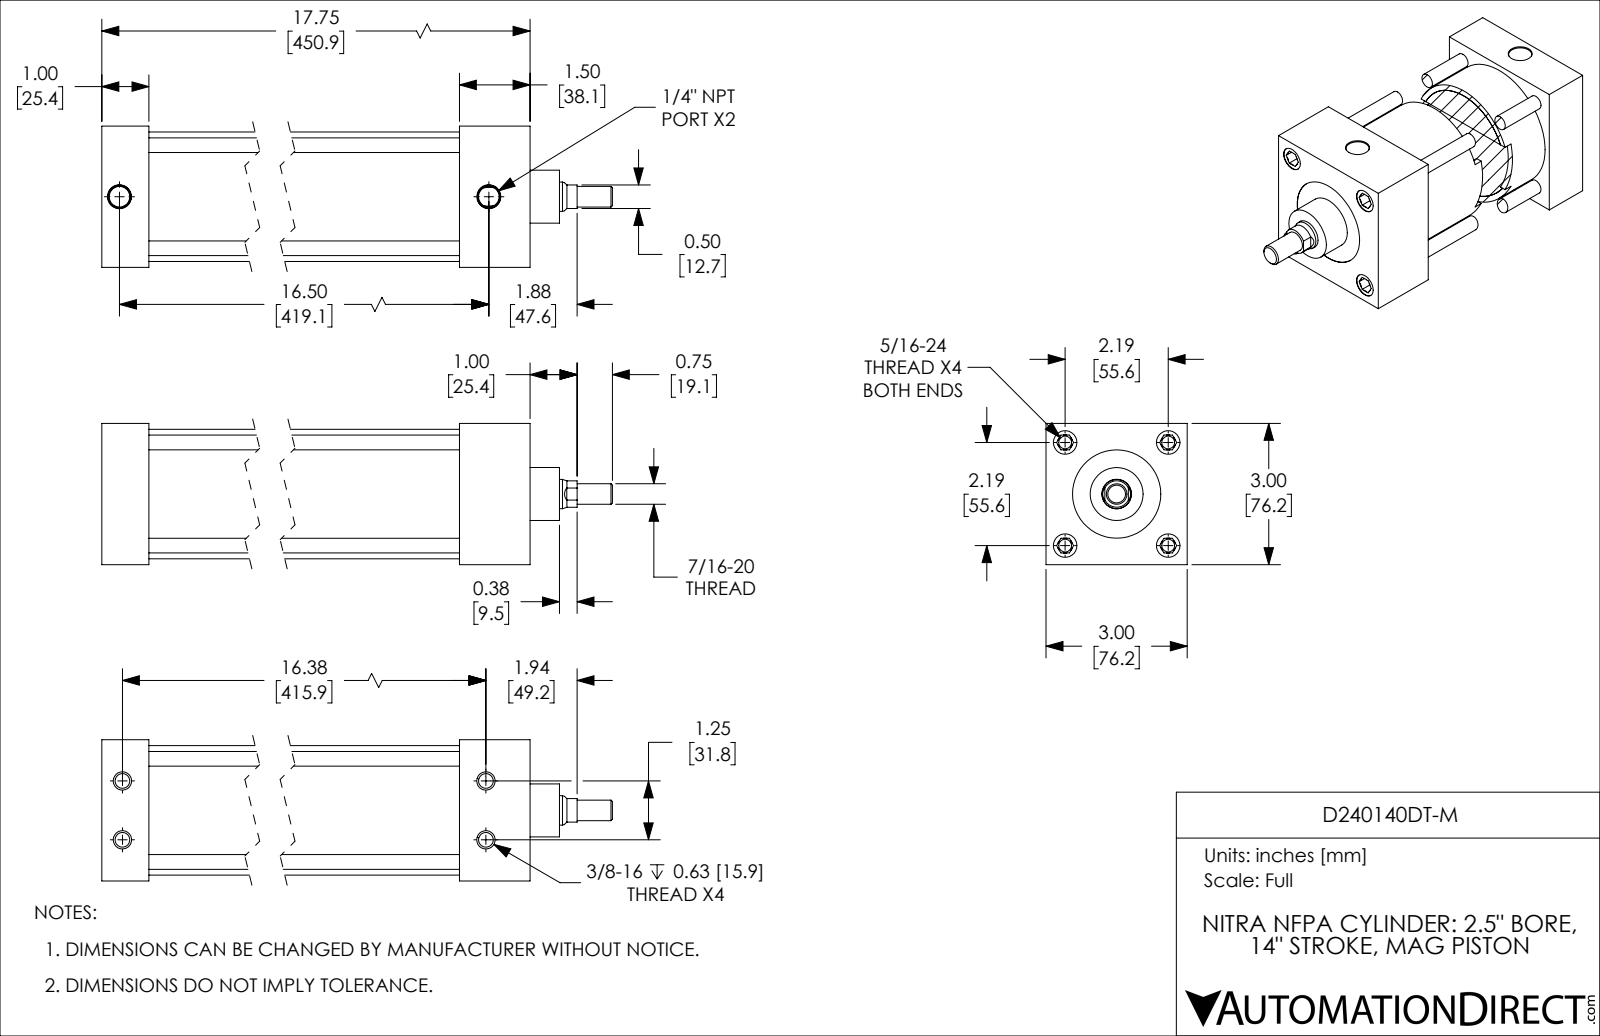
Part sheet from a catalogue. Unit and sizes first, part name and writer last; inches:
Units: inches
Overall size (bounding box): 19.5 × 3 × 3
Round holes (diameter × count): ⌀0.272 ×4, ⌀0.313 ×4, ⌀0.5 ×4, ⌀0.438 ×2, ⌀0.626 ×1, ⌀1.875 ×1, ⌀2.501 ×1
Round bosses / shafts (diameter × count): ⌀0.312 ×4, ⌀2.751 ×1, ⌀2.499 ×1, ⌀1.125 ×1, ⌀0.624 ×1, ⌀0.437 ×1
Partial cylindrical surfaces — rounded edges, fillets, slot ends (radius × count): R0.281 ×1
Main face-to-face distances: 3, 1, 16.25, 15.25, 17.75, 16.75, 1.5, 1.25, 2.25, 14
Hole centre spacings: 1.548, 2.19, 16.449, 0.628, 0.628, 1.25, 3.097, 16.375
Volume: 53.03 in³ · Surface area: 445.5 in²
Bodies: 2 solids, 200 faces (58 planar, 62 cylindrical, 80 other)
Part name (STEP PRODUCT): D240140DT-M; D240140DT-M_PISTON_KK1; D240140DT-M_BODY
STEP written by: SolidWorks 2019 (CONFIG_CONTROL_DESIGN)
